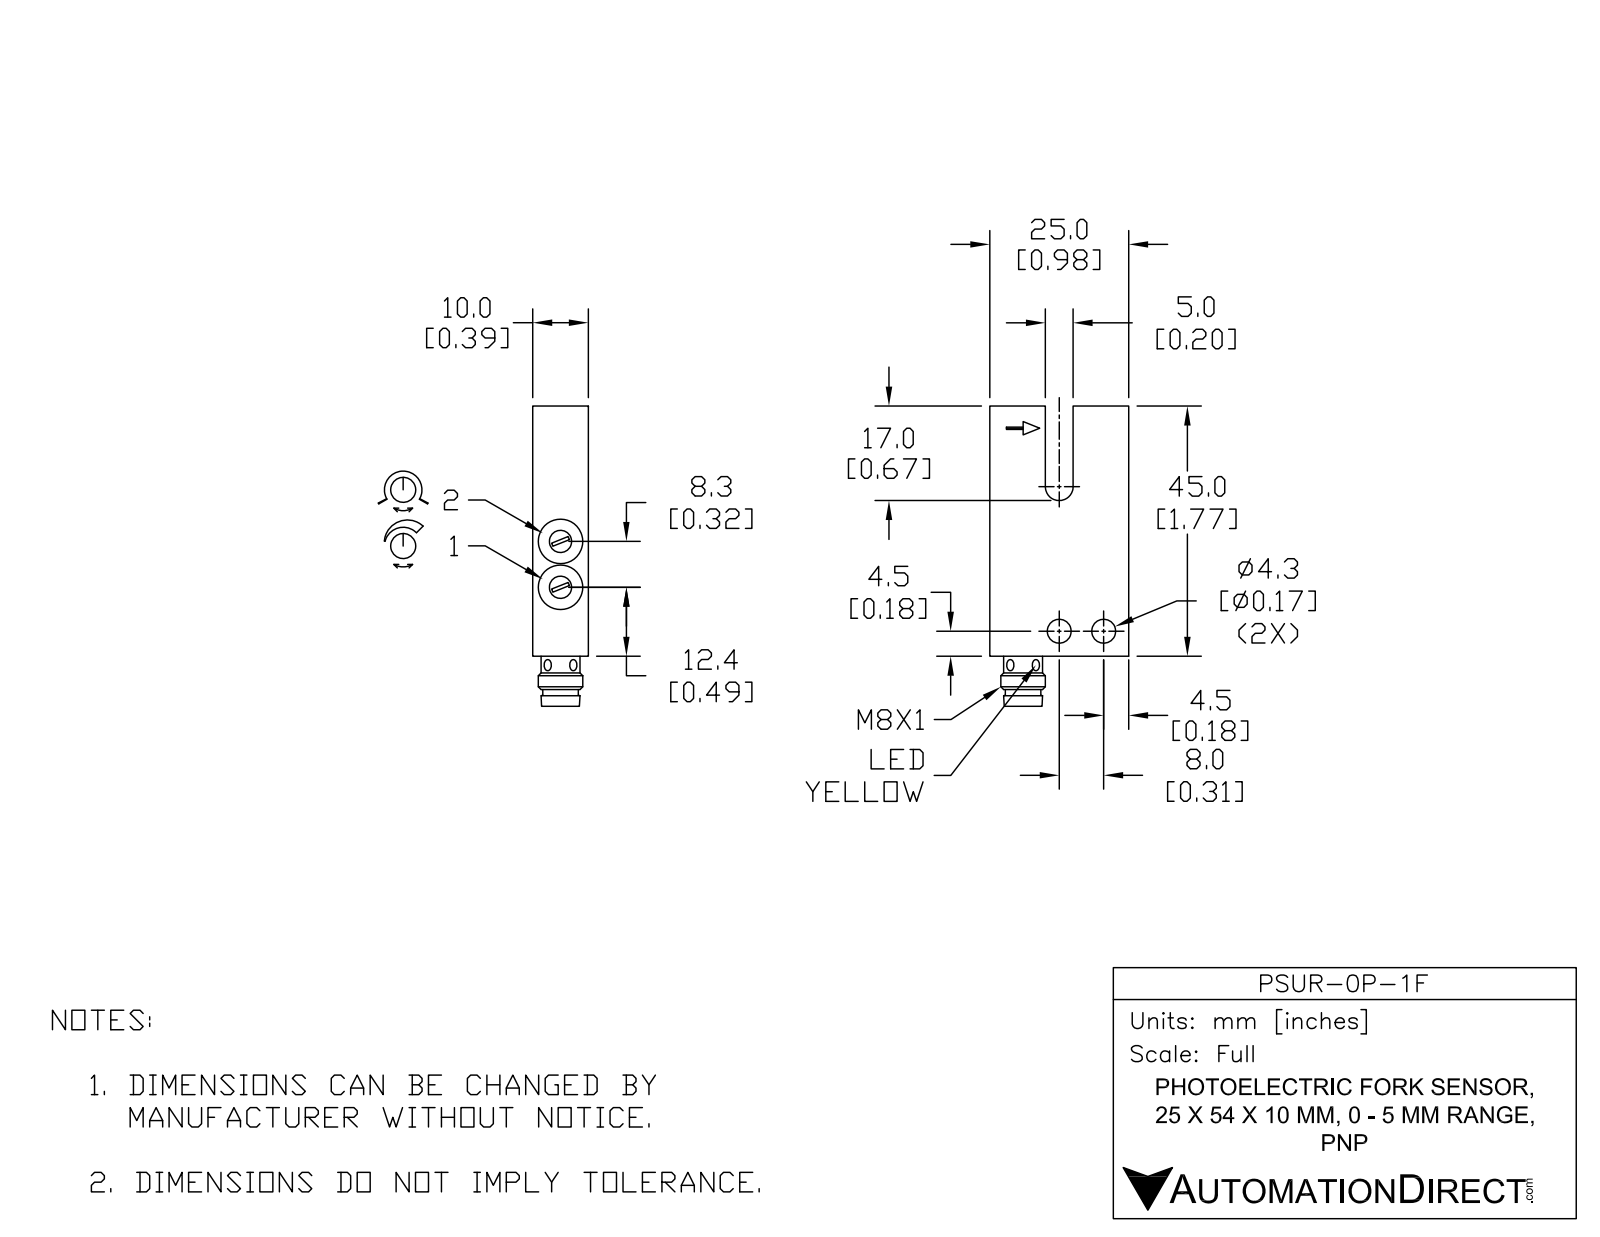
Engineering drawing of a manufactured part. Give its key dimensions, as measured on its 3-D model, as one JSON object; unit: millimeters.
{"part_name": "PSUR-0P-1F", "step_written_by": "SolidWorks 2019 (AUTOMOTIVE_DESIGN)", "units": "millimeters", "bodies": {"solids": 1, "faces": 86, "planar": 34, "cylindrical": 40, "other": 12}, "overall_size": [54, 25, 10], "volume_mm3": 10400, "surface_area_mm2": 4390, "round_holes": [[2, 2], [4, 2], [4.3, 2], [8, 2], [5.8, 1]], "round_bosses_or_shafts": [[1, 3], [8, 1], [6.8, 1]], "partial_cylinders_radius": [[1.6, 2], [2.5, 1]], "face_to_face_distances": [10, 25, 15, 45, 5, 9.9, 24.9, 14.9, 4, 49], "hole_center_spacings": [8, 8.3]}
